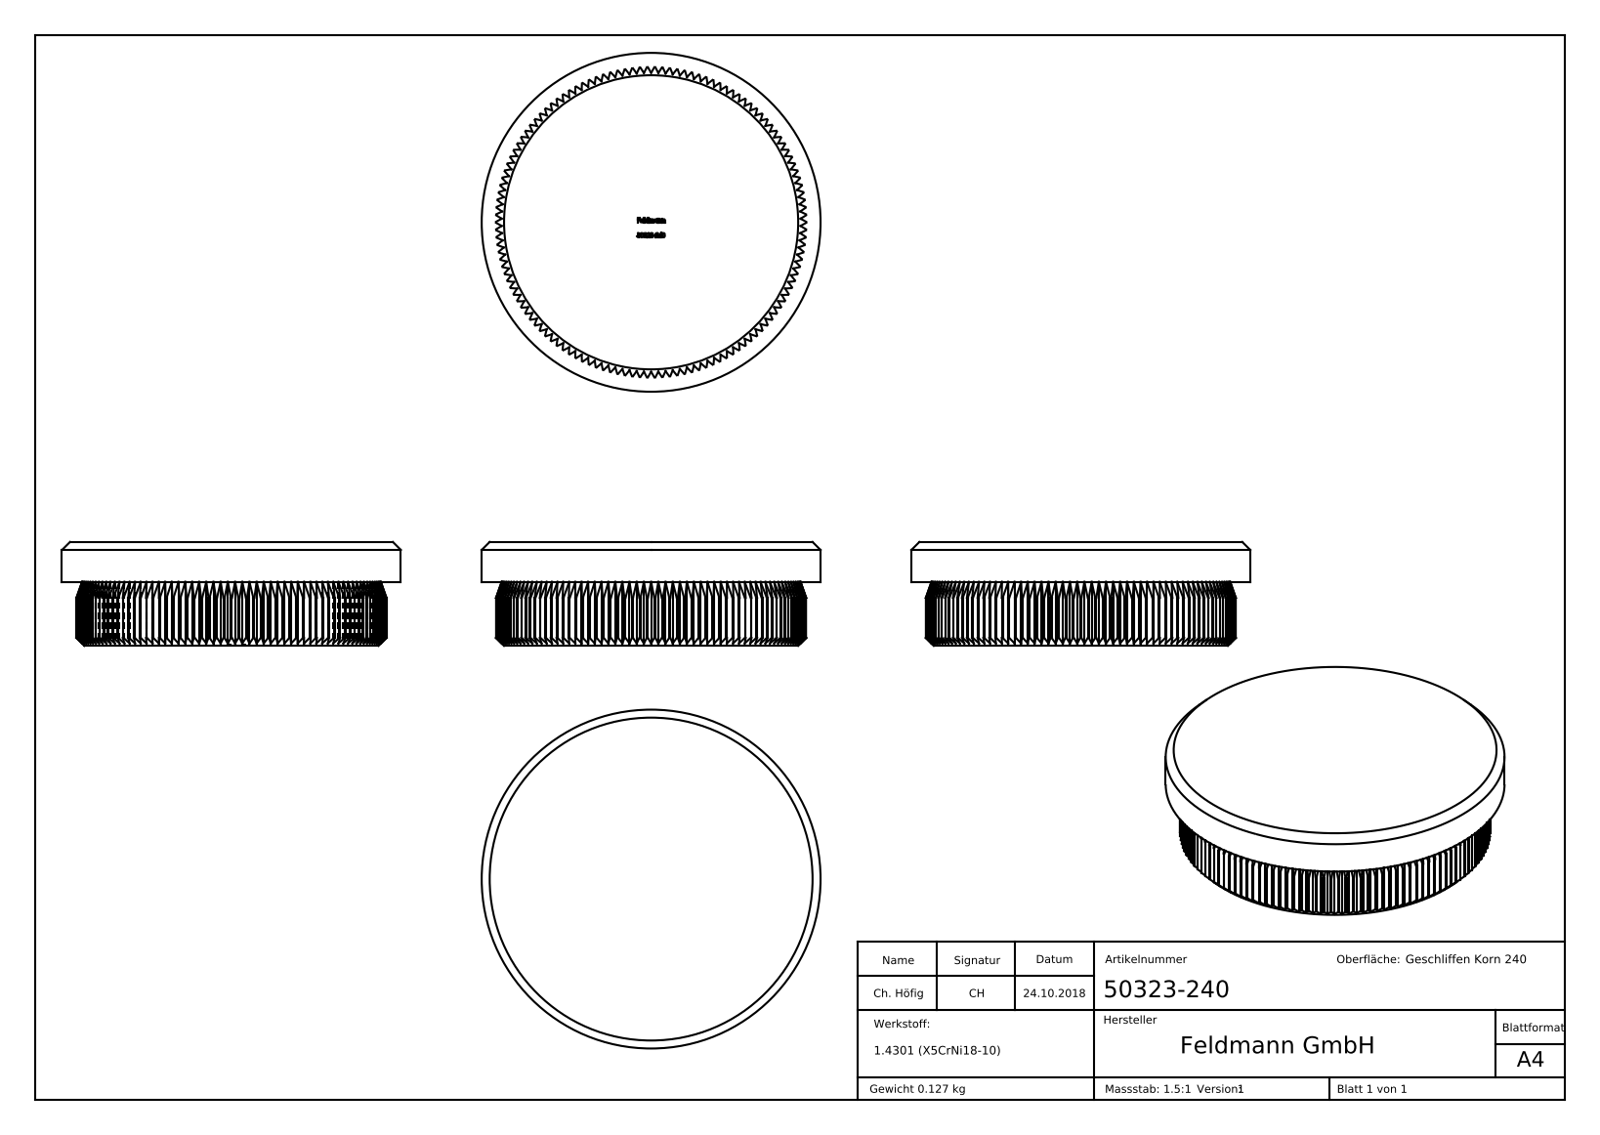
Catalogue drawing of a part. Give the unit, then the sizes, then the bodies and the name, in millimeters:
Units: millimetres
Overall size (bounding box): 42.4 × 42.4 × 13
Round bosses / shafts (diameter × count): ⌀42.4 ×1
Partial cylindrical surfaces — rounded edges, fillets, slot ends (radius × count): R19.4 ×1
Main face-to-face distances: 13, 18.7, 8, 5, 18.72, 18.68, 7.9, 12.9, 1.64, 1.82
Volume: 16 093 mm³ · Surface area: 5 053 mm²
Bodies: 1 solid, 782 faces (401 planar, 132 cylindrical, 249 other)
Part name (STEP PRODUCT): 50323-240
STEP written by: SolidWorks 2015 (CONFIG_CONTROL_DESIGN)
